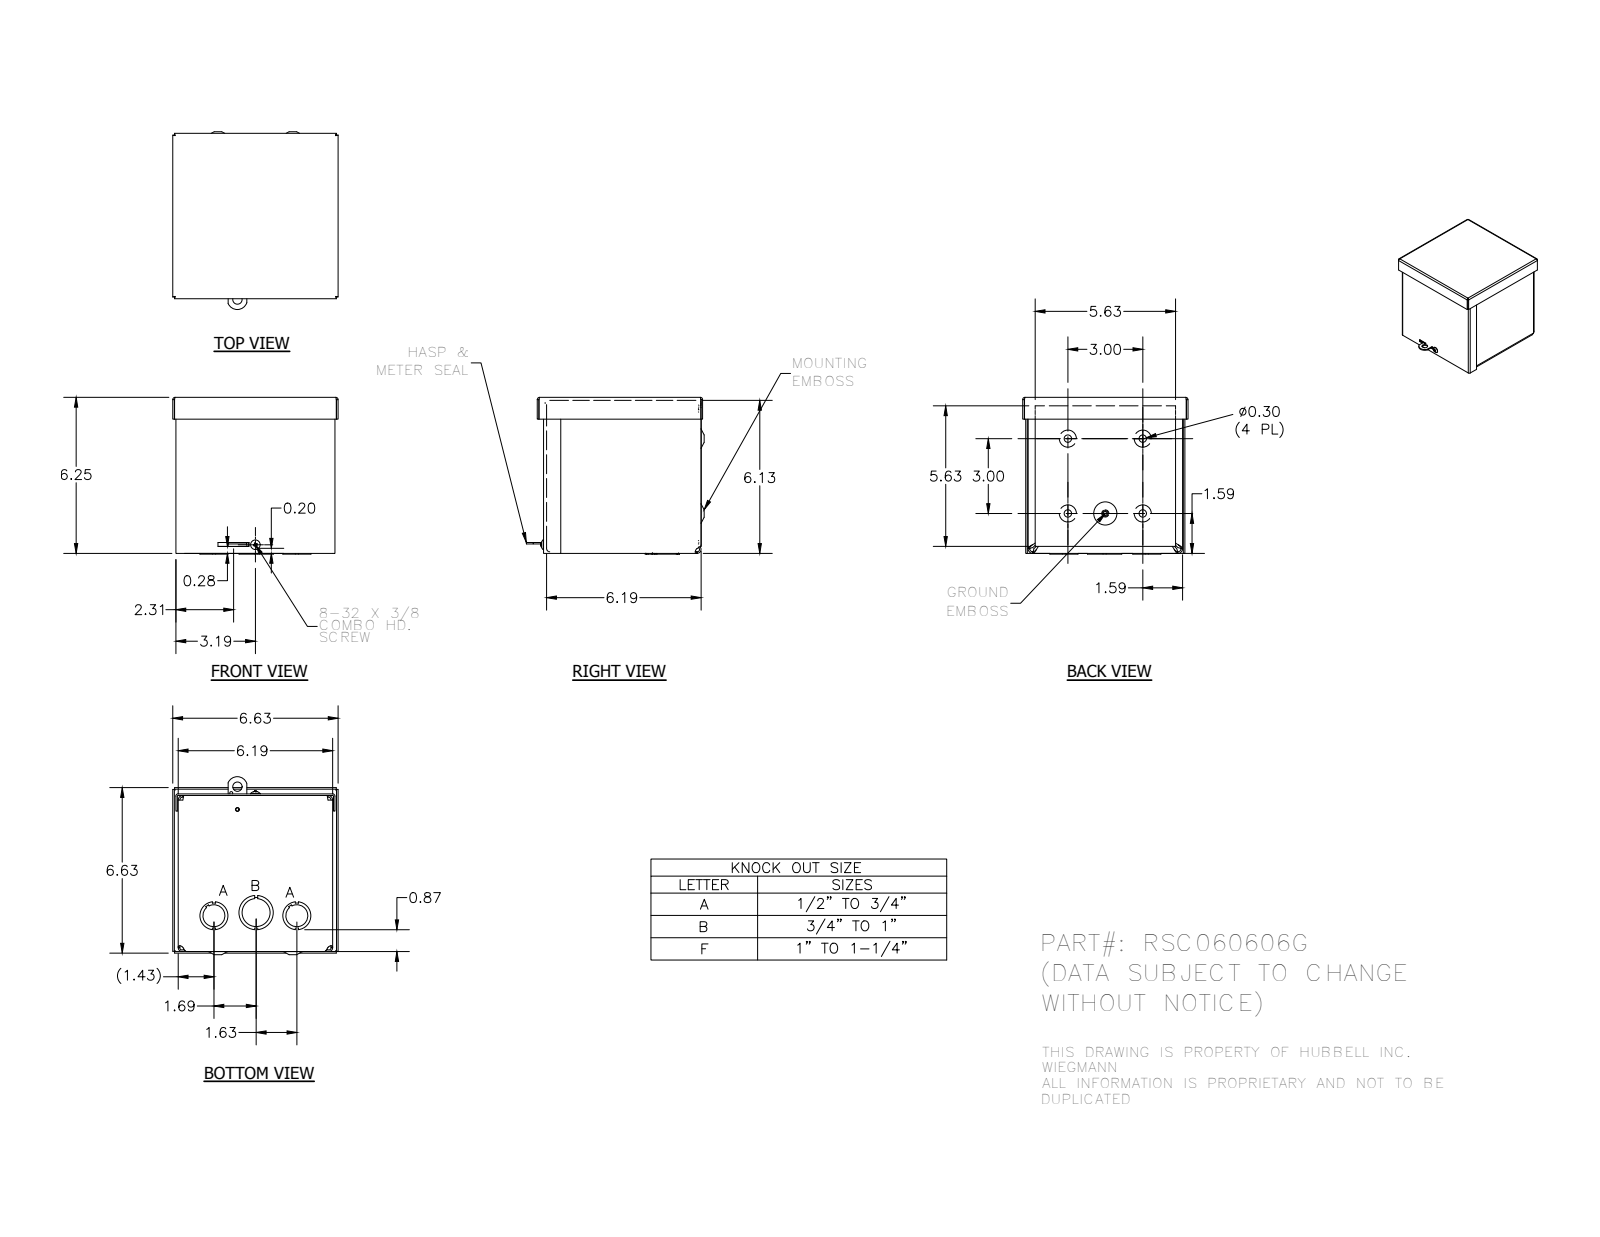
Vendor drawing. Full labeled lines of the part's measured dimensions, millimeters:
Part name (STEP PRODUCT): RSC060606G_WRAP; RSC0606G_LID; RSC0606G_CAP; 3183 (+4 more)
STEP written by: Autodesk Inventor 2014 (AUTOMOTIVE_DESIGN)
Units: millimetres
Bodies: 6 solids, 461 faces (220 planar, 116 cylindrical, 125 other)
Overall size (bounding box): 180.97 × 168.28 × 159.53
Volume: 330 019 mm³ · Surface area: 426 922 mm²
Round holes (diameter × count): ⌀7.62 ×4, ⌀28.57 ×3, ⌀3.17 ×2, ⌀7.95 ×2, ⌀22.22 ×2, ⌀3.76 ×1, ⌀3.96 ×1, ⌀4.19 ×1, ⌀9.52 ×1, ⌀34.92 ×1
Round bosses / shafts (diameter × count): ⌀9.75 ×1, ⌀5.8 ×1, ⌀4.17 ×1
Partial cylindrical surfaces — rounded edges, fillets, slot ends (radius × count): R0.25 ×10, R0.79 ×8, R2.37 ×8, R3.17 ×8, R4.75 ×8, R0.53 ×4, R0.79 ×4, R1.4 ×4
Main face-to-face distances: 1.58, 155.59, 1.57, 157.17, 158.74, 3.15, 157.16, 158.73, 154.01, 157.15
Hole centre spacings: 76.2, 38.1, 85.19, 107.76, 9.1, 17.84, 23.19, 31.79
